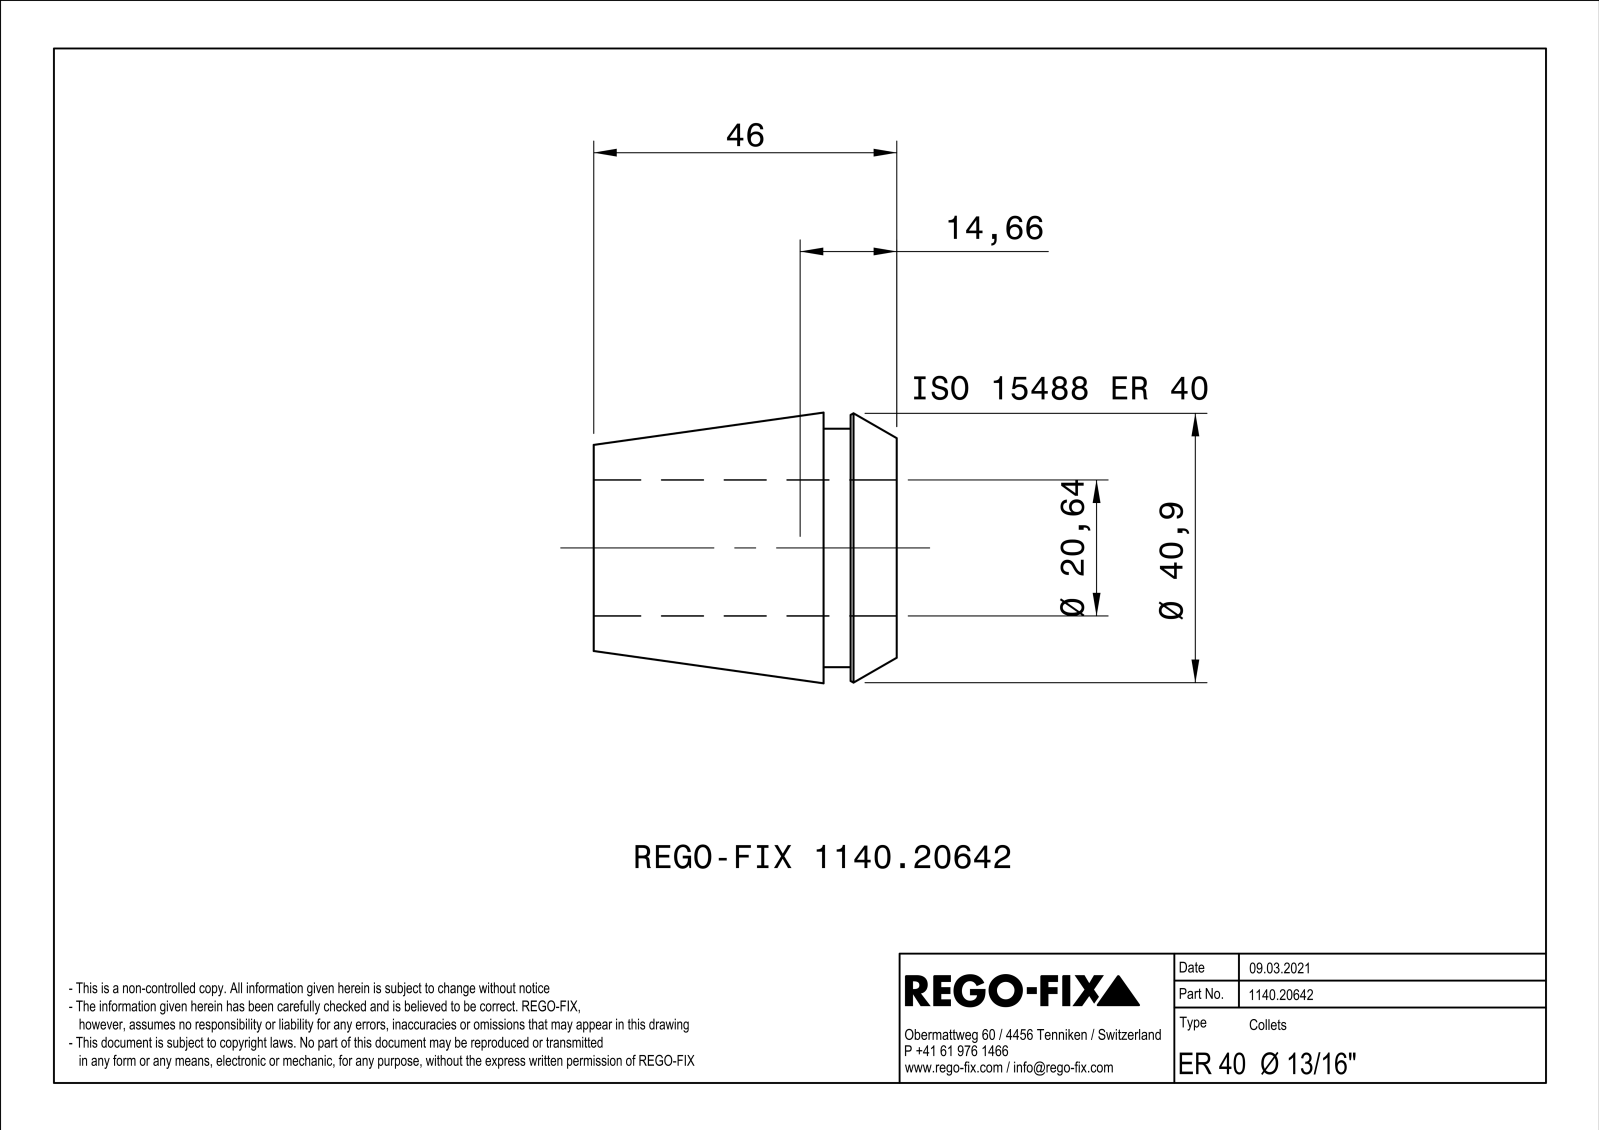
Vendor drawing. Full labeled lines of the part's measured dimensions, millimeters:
Part name (STEP PRODUCT): NOCUT
STEP written by: SIEMENS PLM Software Solid Edge ST10 (AUTOMOTIVE_DESIGN)
Units: millimetres
Bodies: 1 solid, 177 faces (88 planar, 9 cylindrical, 80 other)
Overall size (bounding box): 46 × 40.99 × 40.99
Volume: 27 337 mm³ · Surface area: 18 720 mm²
Round holes (diameter × count): ⌀20.64 ×1
Round bosses / shafts (diameter × count): ⌀36.2 ×1
Main face-to-face distances: 1, 46, 11.1, 34.9, 7, 4.1, 39, 7.5, 0.5, 3.6
